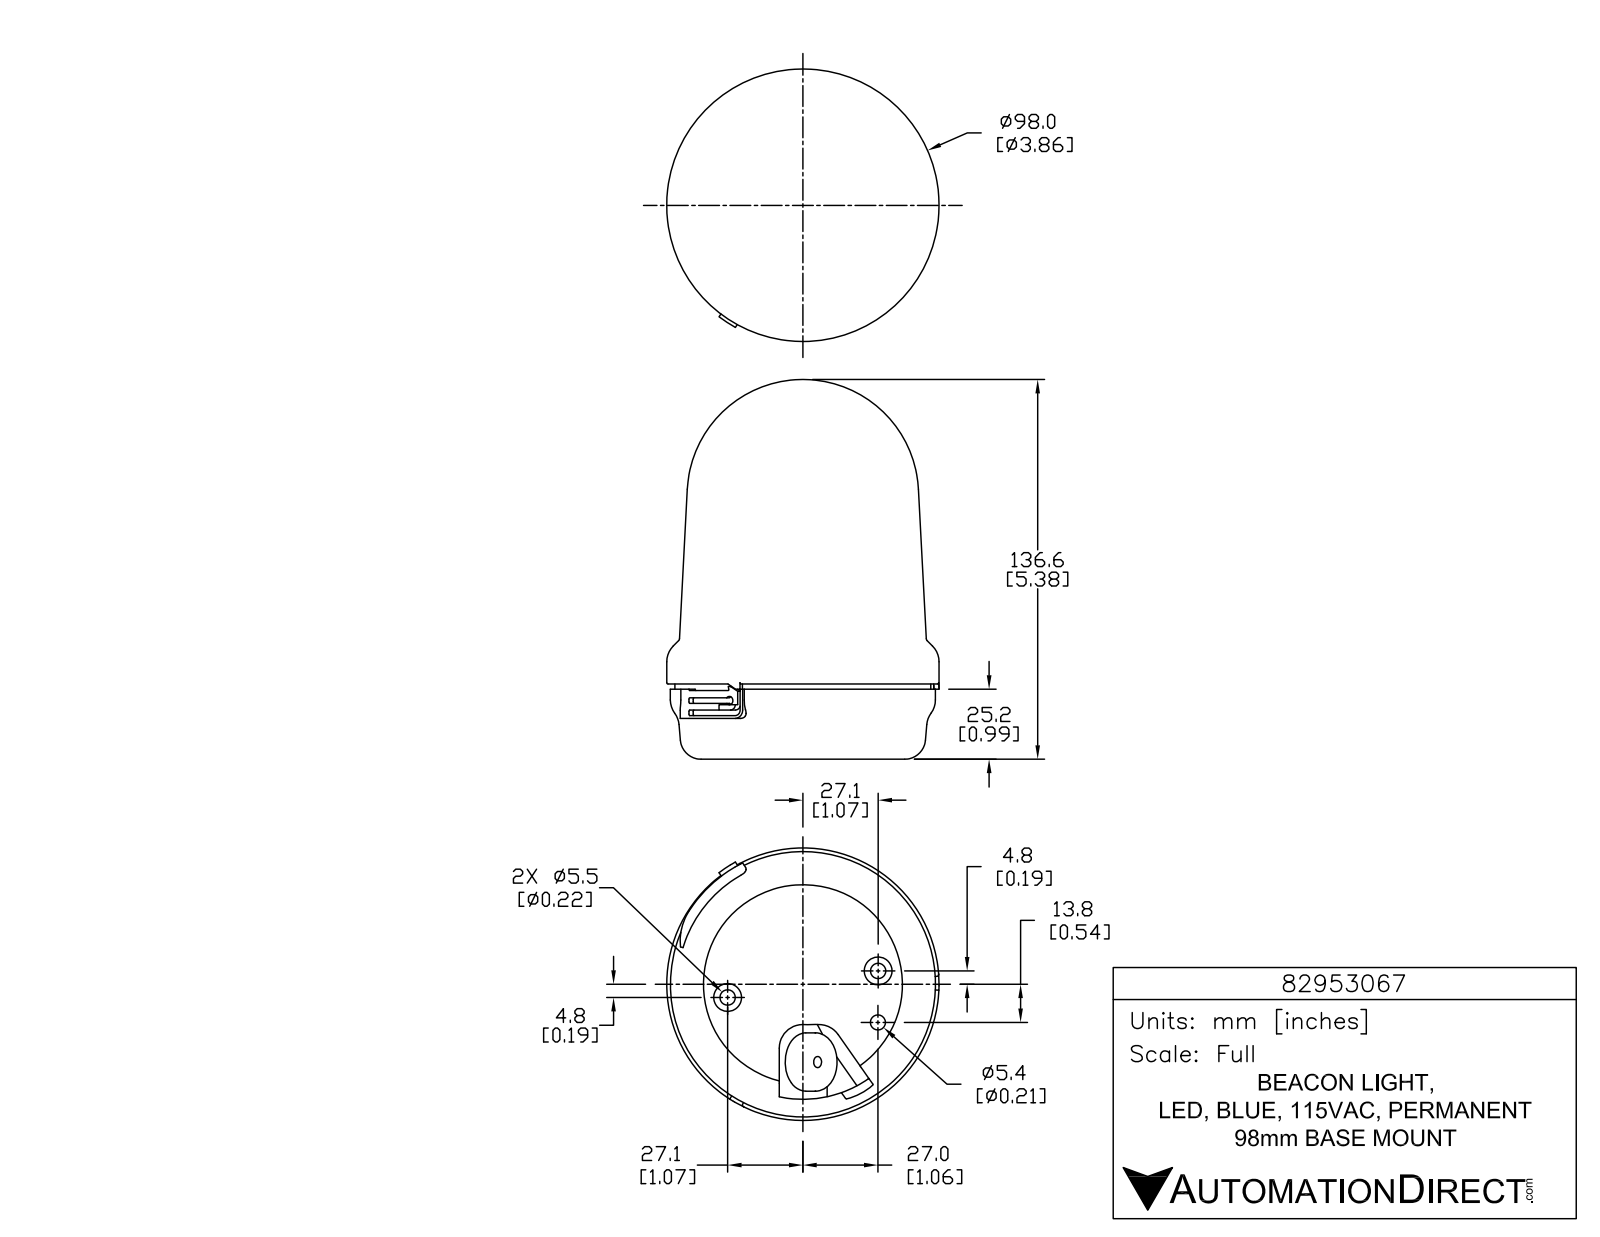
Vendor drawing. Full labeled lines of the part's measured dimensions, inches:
Part name (STEP PRODUCT): 82953067
STEP written by: SolidWorks 2015 (AUTOMOTIVE_DESIGN)
Units: inches
Bodies: 1 solid, 872 faces (566 planar, 204 cylindrical, 102 other)
Overall size (bounding box): 5.378 × 3.858 × 3.858
Volume: 44.69 in³ · Surface area: 73.66 in²
Round holes (diameter × count): ⌀0.059 ×3, ⌀0.217 ×2, ⌀0.157 ×1, ⌀0.213 ×1, ⌀2.819 ×1
Round bosses / shafts (diameter × count): ⌀0.339 ×3, ⌀0.084 ×3, ⌀0.394 ×2, ⌀3.858 ×1, ⌀3.756 ×1, ⌀3.626 ×1, ⌀0.827 ×1
Partial cylindrical surfaces — rounded edges, fillets, slot ends (radius × count): R0.005 ×9, R0.005 ×6, R0.012 ×6, R0.012 ×6, R0.012 ×6, R0.196 ×6, R0.02 ×5, R0.039 ×4
Main face-to-face distances: 1.045, 0.972, 0.073, 0.02, 0.992, 1.065, 0.236, 0.579, 0.559, 0.413
Hole centre spacings: 1.083, 0.73, 1.193, 2.158, 2.165
